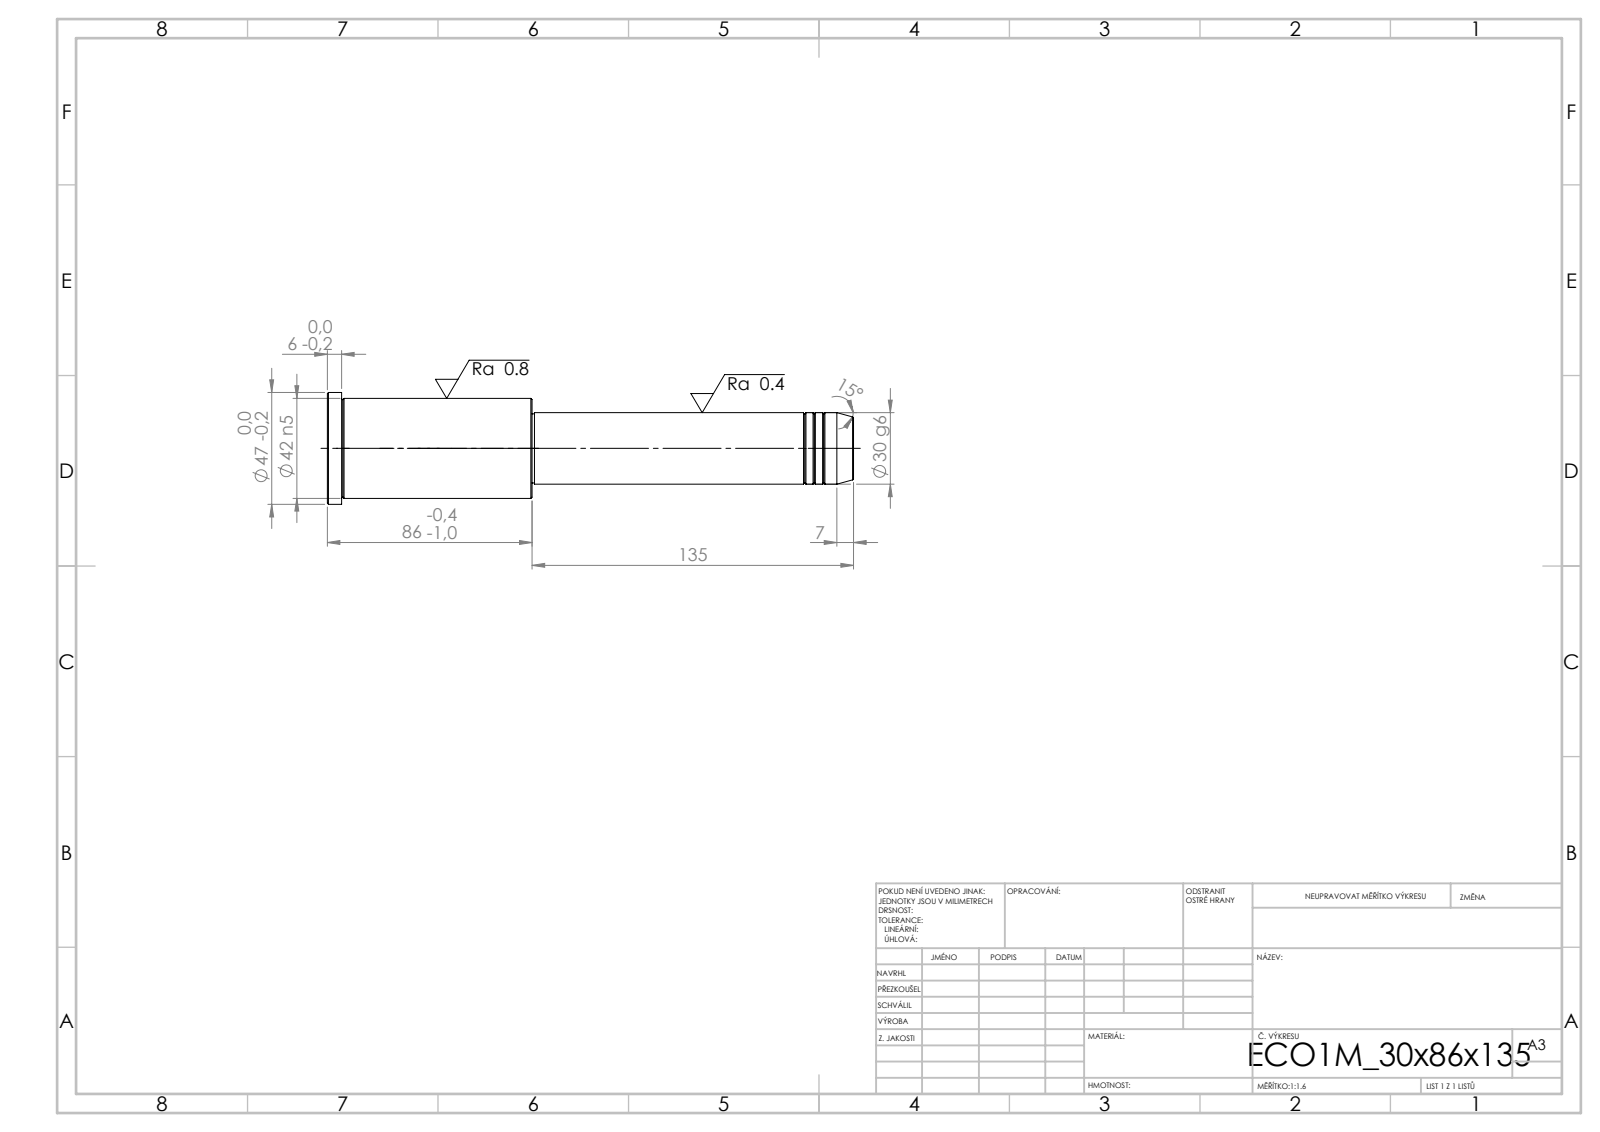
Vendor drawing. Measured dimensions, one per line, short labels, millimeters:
written by: SolidWorks 2019 (CONFIG_CONTROL_DESIGN)
unit: mm
bodies: 1 solid, 43 faces (5 planar, 14 cylindrical, 24 other)
size: 221 × 47 × 47
volume: 215 834 mm³; area: 27 672 mm²
bosses: 1× ⌀47, 1× ⌀42, 1× ⌀30, 1× ⌀29
face distances: 86, 135, 221, 215, 80, 6, 134, 1, 81, 87
